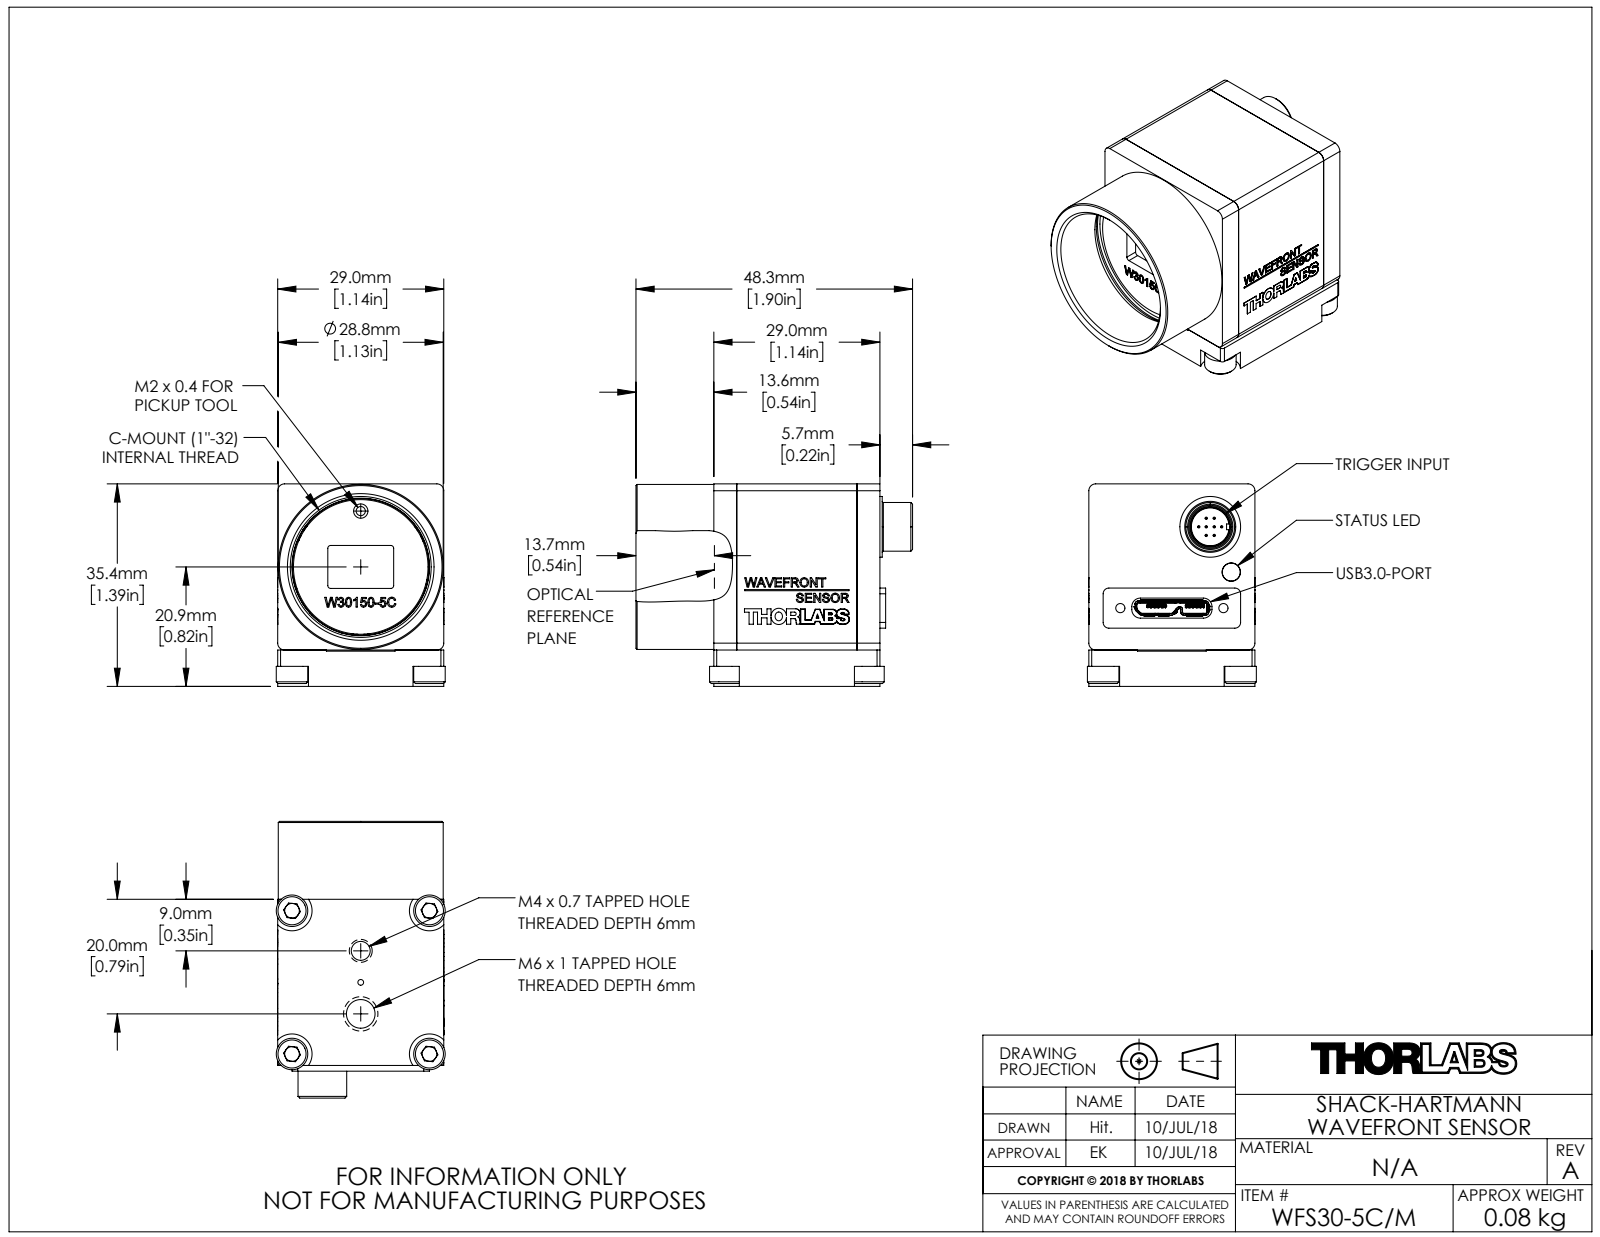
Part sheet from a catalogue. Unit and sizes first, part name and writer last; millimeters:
Units: millimetres
Overall size (bounding box): 48.3 × 35.35 × 29.5
Round holes (diameter × count): ⌀3.2 ×11, ⌀2.5 ×5, ⌀1.6 ×3, ⌀1.9 ×3, ⌀0.95 ×1, ⌀1 ×1, ⌀1.5 ×1, ⌀3.3 ×1, ⌀5 ×1, ⌀6.8 ×1, ⌀8 ×1, ⌀15 ×1
Round bosses / shafts (diameter × count): ⌀0.4 ×8, ⌀1 ×6, ⌀3 ×5, ⌀5.5 ×4, ⌀28.8 ×1, ⌀23.9 ×1, ⌀23.5 ×1, ⌀15.4 ×1
Partial cylindrical surfaces — rounded edges, fillets, slot ends (radius × count): R0.5 ×37, R0.2 ×31, R0.15 ×29, R0.3 ×12, R1 ×11, R1.5 ×10, R0.1 ×8, R0.6 ×8
Main face-to-face distances: 29, 0.6, 28.4, 6.35, 4.8, 35.35, 2.62, 27.8, 17.57, 22.37
Hole centre spacings: 9.75, 18.83, 9.74, 13.79, 16.88, 5.04, 13.89, 17.33
Bodies: 0 solids, 2595 faces (1880 planar, 404 cylindrical, 311 other)
Part name (STEP PRODUCT): MTN008519-E0W
STEP written by: SolidWorks 2016 (AUTOMOTIVE_DESIGN)
